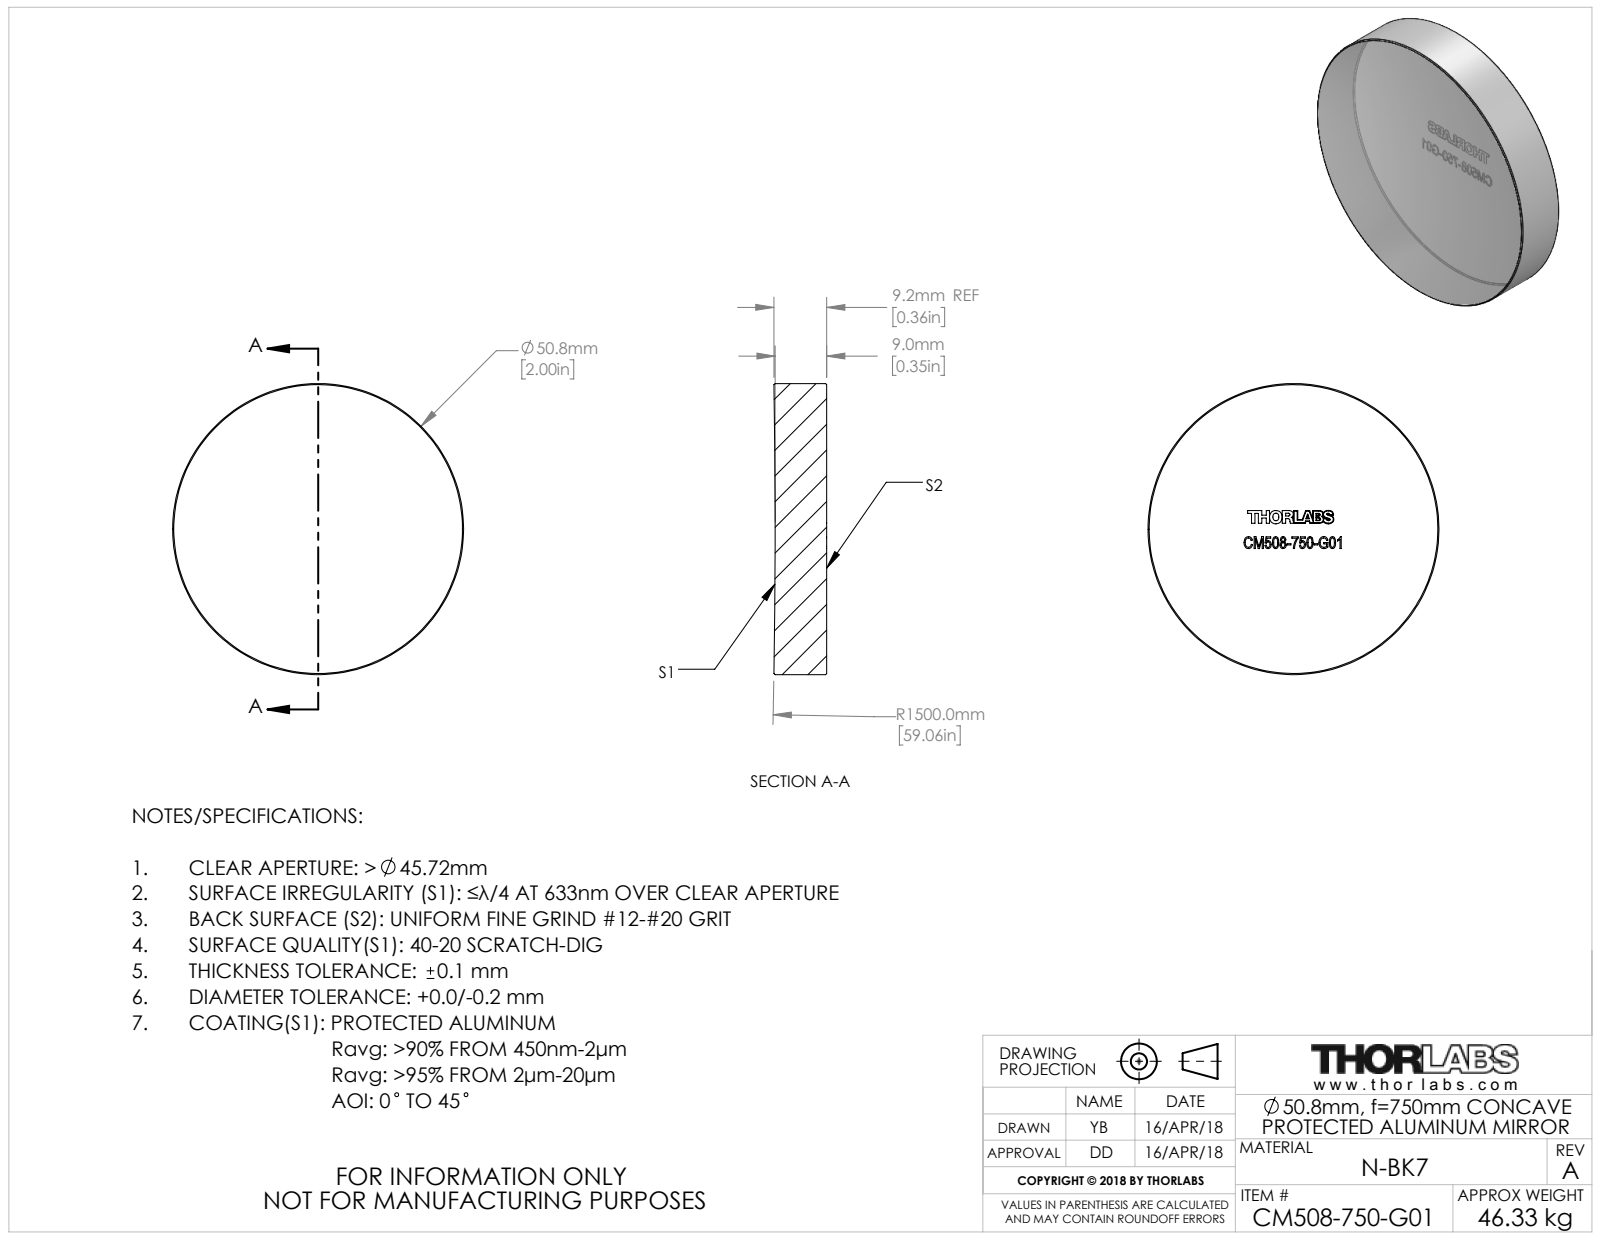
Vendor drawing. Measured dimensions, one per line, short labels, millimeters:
name: TTN153330-E0W
written by: SolidWorks 2018 (CONFIG_CONTROL_DESIGN)
unit: mm
bodies: 1 solid, 42 faces (34 planar, 2 cylindrical, 6 other)
size: 50.8 × 50.8 × 9.21
volume: 18 453 mm³; area: 5 487 mm²
bosses: 1× ⌀50.8
